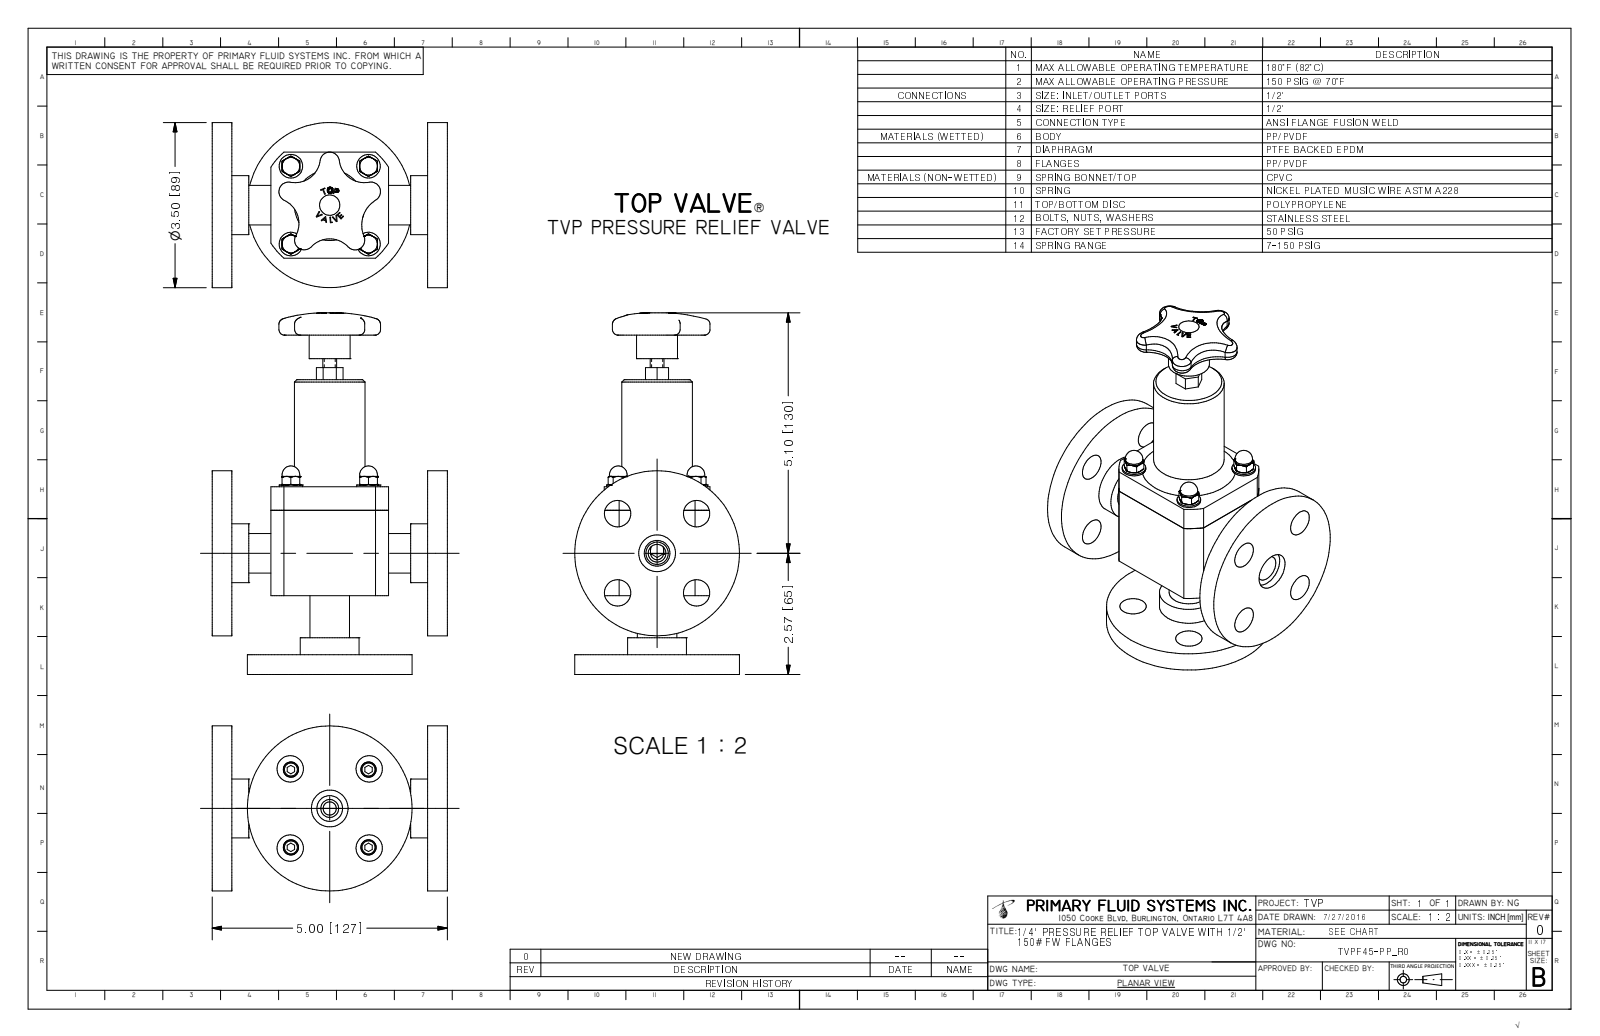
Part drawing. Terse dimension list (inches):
name: TVPF45-PP_R0
written by: Autodesk Inventor 2009 (AUTOMOTIVE_DESIGN)
unit: in
bodies: 1 solid, 392 faces (159 planar, 72 cylindrical, 161 other)
size: 7.67 × 5 × 3.5
volume: 29.82 in³; area: 147.1 in²
holes: 8× ⌀0.56, 4× ⌀0.147, 2× ⌀0.546, 2× ⌀0.78, 1× ⌀1.525
bosses: 4× ⌀0.5, 4× ⌀0.375, 4× ⌀0.312, 2× ⌀3.5, 2× ⌀1.25, 2× ⌀0.84, 1× ⌀1.5, 1× ⌀0.87
rounds: 5× R0.085, 5× R0.205, 4× R0.536, 4× R0.656, 1× R0.625, 1× R0.745, 1× R1.488
face distances: 0.42, 4.58, 1.25, 5, 4.16, 3.75, 0.83, 3.33, 2.25, 1.67
hole spacings: 1.188, 1.68, 1.665, 2.375, 0.02, 0.021, 1.167, 1.167
